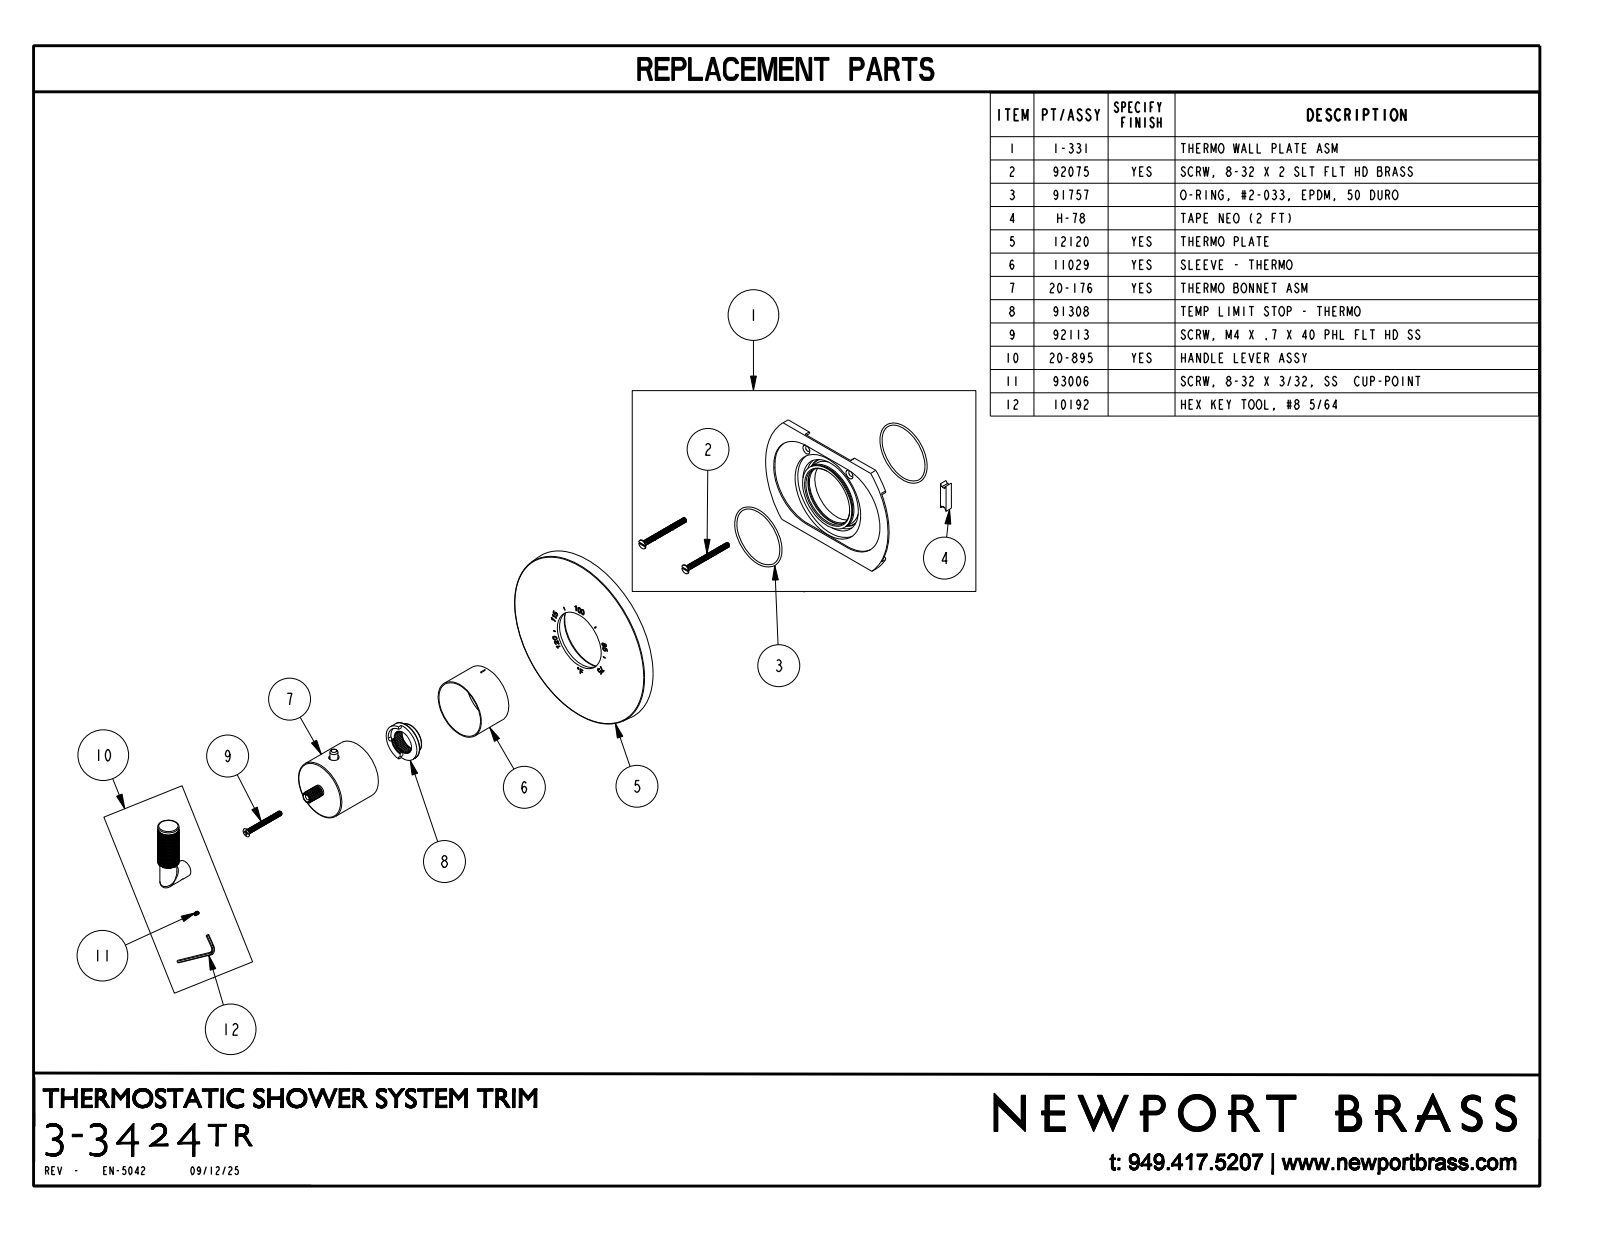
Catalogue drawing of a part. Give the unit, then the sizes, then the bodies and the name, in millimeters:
Units: millimetres
Overall size (bounding box): 152.4 × 152.2 × 101.4
Round holes (diameter × count): ⌀50.8 ×1
Round bosses / shafts (diameter × count): ⌀14 ×2, ⌀50 ×1, ⌀17.5 ×1, ⌀17.4 ×1, ⌀6.6 ×1
Partial cylindrical surfaces — rounded edges, fillets, slot ends (radius × count): R24.3 ×1, R73.9 ×1
Main face-to-face distances: 9.5, 73.6, 64.1, 9.2, 0.3, 64.4, 7.2, 2, 2.3, 66.4
Volume: 311 700 mm³ · Surface area: 55 630 mm²
Bodies: 1 solid, 4258 faces (111 planar, 773 cylindrical, 3374 other)
Part name (STEP PRODUCT): 3-3424TR
STEP written by: CREO PARAMETRIC BY PTC INC, 2025093 (CONFIG_CONTROL_DESIGN)
